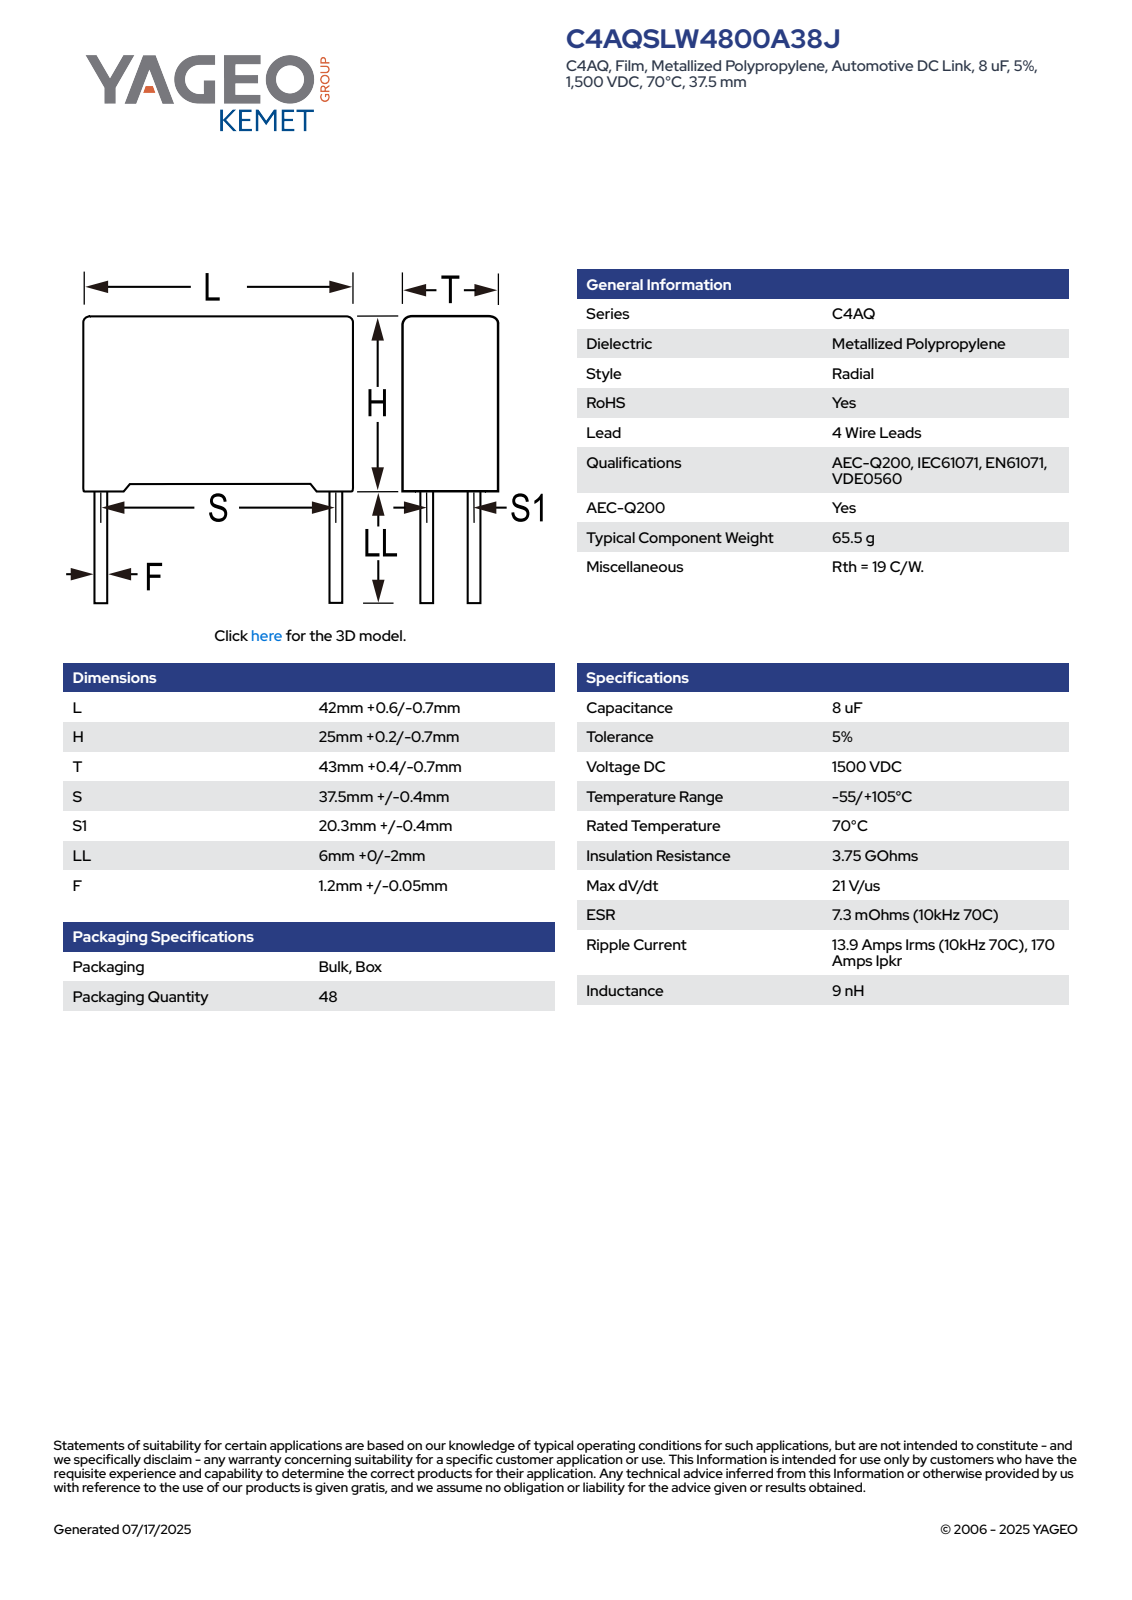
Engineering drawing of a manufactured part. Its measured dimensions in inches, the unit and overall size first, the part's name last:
Units: inches
Overall size (bounding box): 1.709 × 1.677 × 1.228
Round bosses / shafts (diameter × count): ⌀0.049 ×4
Main face-to-face distances: 0.963, 1.677, 1.709, 0.029, 0.992, 0.105, 1.709, 1.572, 1.467, 1.604
Volume: 2.774 in³ · Surface area: 12.83 in²
Bodies: 4 solids, 91 faces (83 planar, 8 cylindrical, 0 other)
Part name (STEP PRODUCT): CFP_RB4_42X25X43_L42.6H25.2T43.4S37.5S120.3LL6F1.25
STEP written by: SolidWorks 2014 (AUTOMOTIVE_DESIGN)
